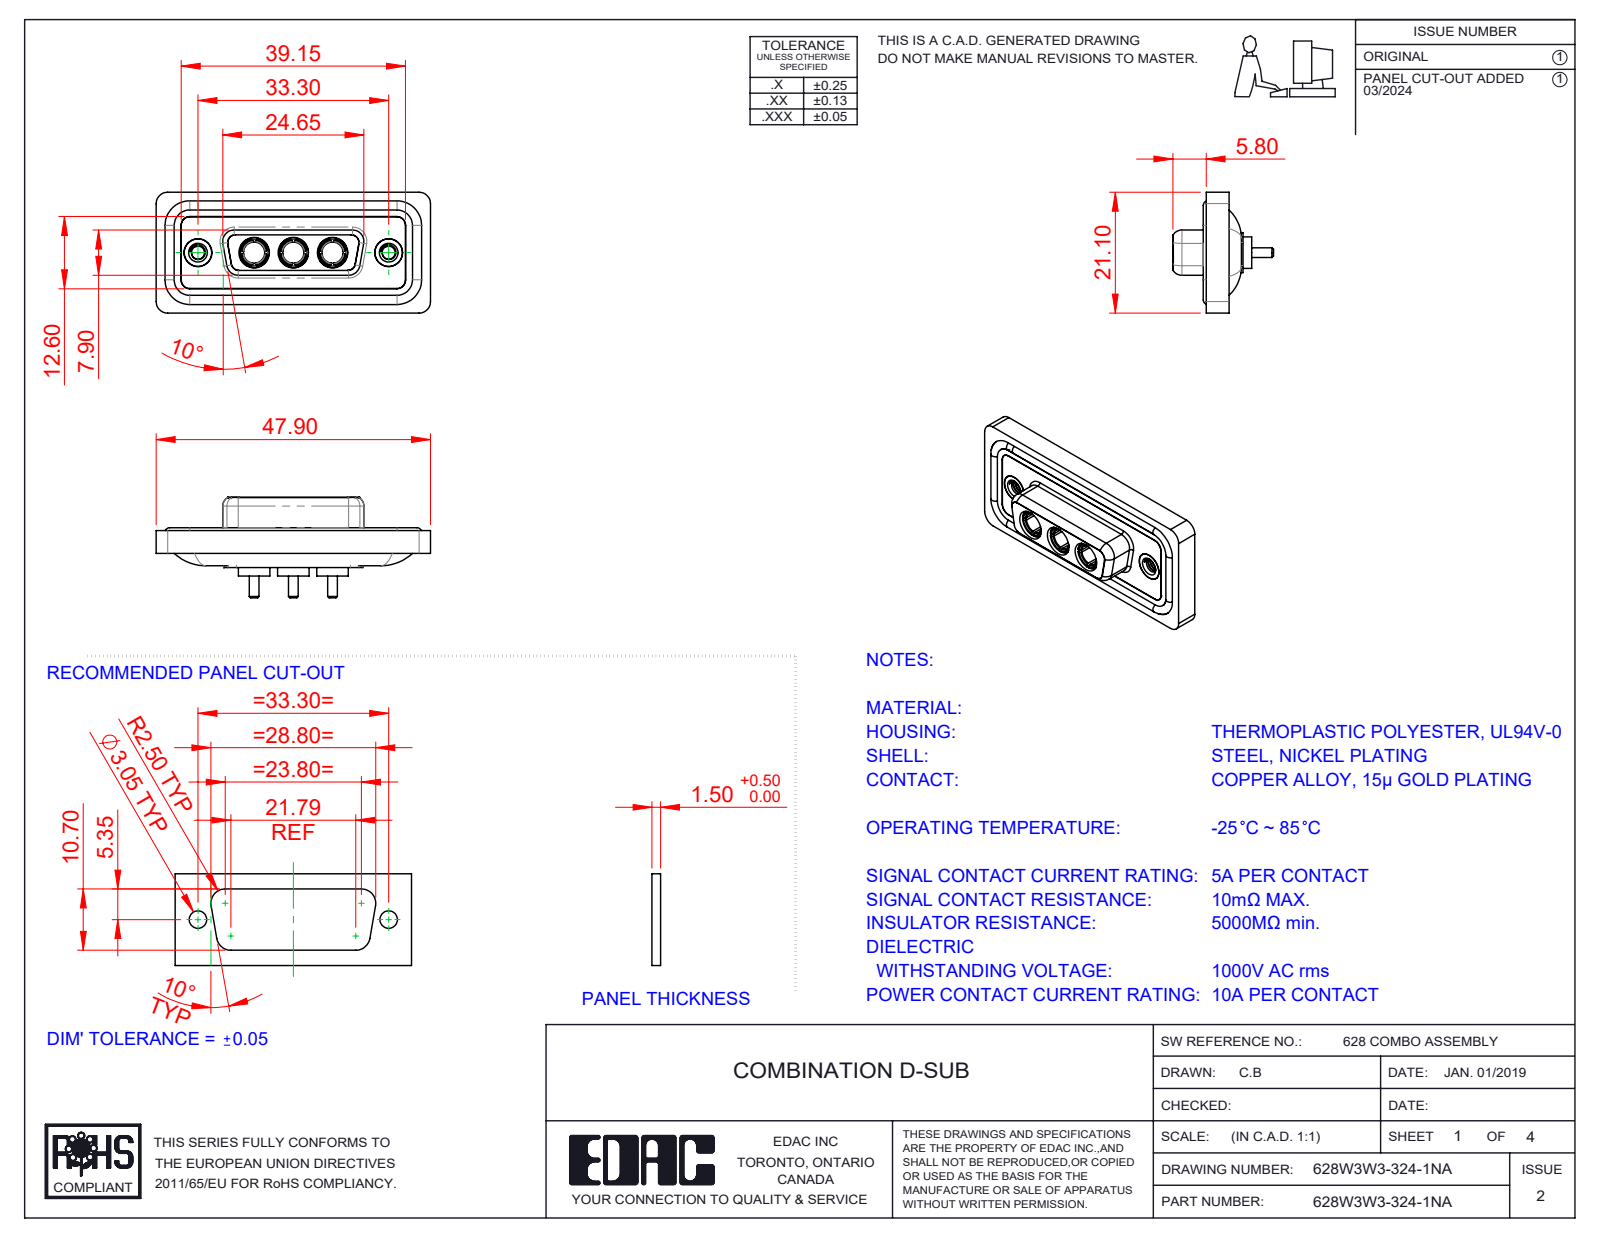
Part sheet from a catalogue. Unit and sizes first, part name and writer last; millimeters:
Units: millimetres
Overall size (bounding box): 47.9 × 21.1 × 17.55
Round holes (diameter × count): ⌀4.85 ×5, ⌀3.7 ×3, ⌀5.3 ×3, ⌀2.26 ×2, ⌀4 ×2, ⌀4.05 ×2, ⌀5 ×2
Round bosses / shafts (diameter × count): ⌀1.6 ×4, ⌀5.5 ×3, ⌀5.2 ×3, ⌀4.96 ×3, ⌀4.75 ×3, ⌀3.75 ×3, ⌀1.7 ×3, ⌀4.95 ×2
Partial cylindrical surfaces — rounded edges, fillets, slot ends (radius × count): R1.5 ×22, R2 ×20, R1.35 ×12, R1.6 ×8, R0.25 ×4, R0.5 ×4, R0.6 ×4, R0.65 ×4
Main face-to-face distances: 0.4, 1.8, 1.6, 0.5, 7.45, 1.1, 2.9, 5.65, 7.05, 1.5
Hole centre spacings: 6.85, 9.8, 16.65, 23.5, 13.7, 33.3
Volume: 5 984 mm³ · Surface area: 9 698 mm²
Bodies: 13 solids, 606 faces (192 planar, 259 cylindrical, 155 other)
Part name (STEP PRODUCT): 628Combo Shell Rear_15 Contacts; 628Combo Waterproof Housing_15 Contacts; 628W3W3-324-1NA; 628Combo Shell Front_15 Contacts (+3 more)
STEP written by: SolidWorks 2023 (CONFIG_CONTROL_DESIGN)
